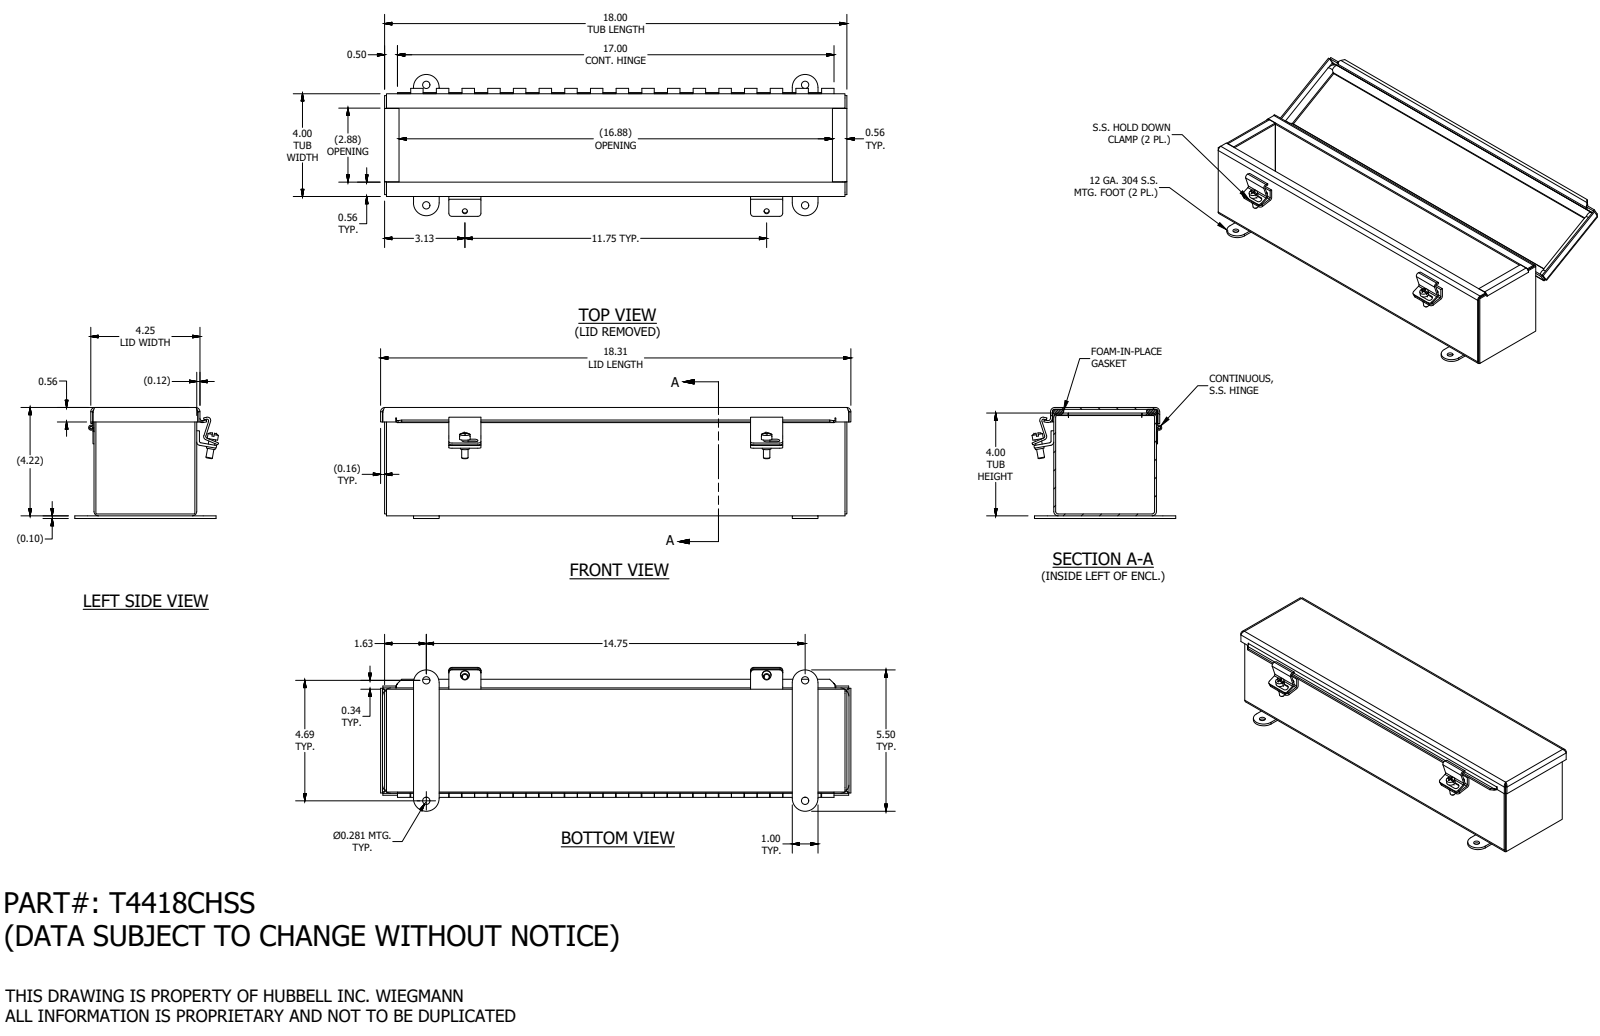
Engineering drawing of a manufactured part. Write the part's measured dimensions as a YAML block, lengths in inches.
part_name: "T4418CHSS"
step_written_by: "SolidWorks 2019 (AUTOMOTIVE_DESIGN)"
units: inches
bodies: {solids: 16, faces: 466, planar: 281, cylindrical: 153, other: 32}
overall_size: [18.313, 5.598, 4.322]
volume: 33.3
surface_area: 881.4
round_holes:
  - {diameter: 0.11, count: 4}
  - {diameter: 0.281, count: 4}
  - {diameter: 0.196, count: 2}
  - {diameter: 0.116, count: 1}
round_bosses_or_shafts:
  - {diameter: 0.41, count: 2}
  - {diameter: 0.344, count: 2}
  - {diameter: 0.25, count: 2}
  - {diameter: 0.2, count: 1}
  - {diameter: 0.1, count: 1}
partial_cylinders:
  - {radius: 0.094, count: 11}
  - {radius: 0.168, count: 11}
  - {radius: 0.085, count: 8}
  - {radius: 0.125, count: 8}
  - {radius: 0.133, count: 4}
  - {radius: 0.242, count: 4}
  - {radius: 0.5, count: 4}
  - {radius: 0.063, count: 3}
face_to_face_distances: [0.074, 3.926, 4.144, 4, 3.852, 4.218, 4.07, 0.218, 17.926, 4.052]
hole_center_spacings: [0.75, 4.687, 11.75, 14.75, 15.476, 11, 11.75, 12.5]
